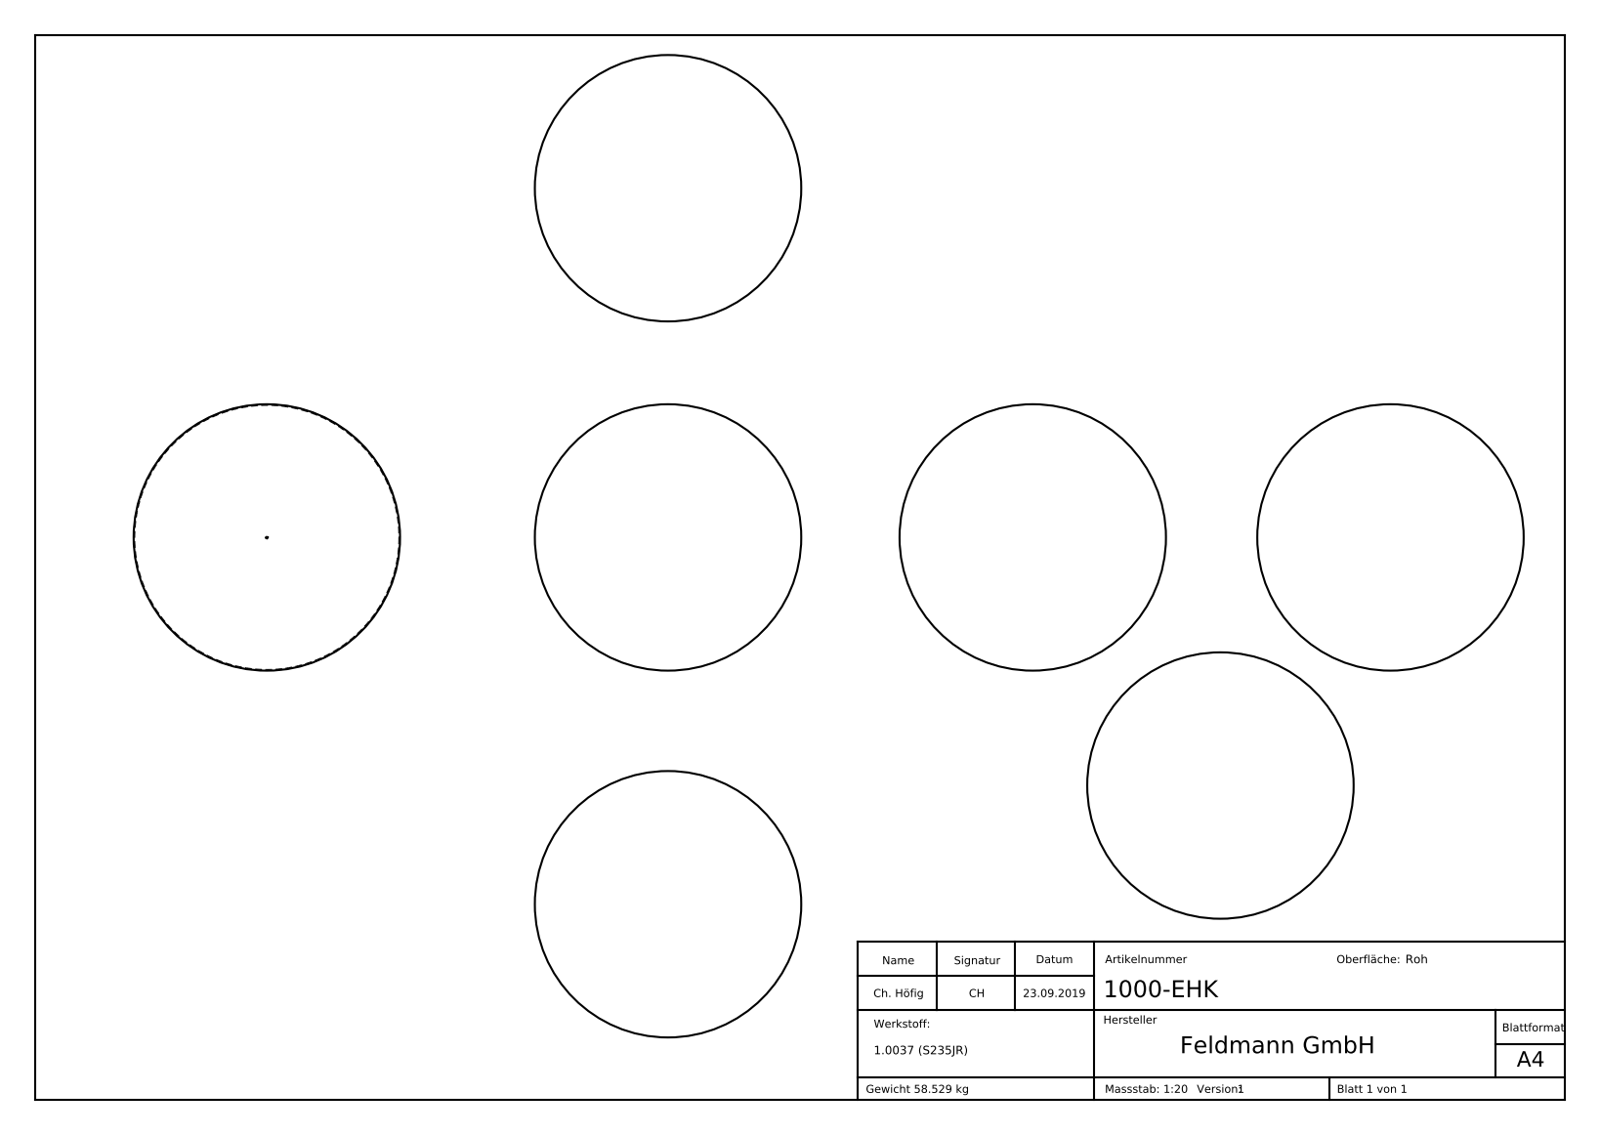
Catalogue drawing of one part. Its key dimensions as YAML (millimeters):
part_name: "1000-EHK"
step_written_by: "SolidWorks 2015 (CONFIG_CONTROL_DESIGN)"
units: millimeters
bodies: {solids: 1, faces: 201, planar: 99, cylindrical: 0, other: 102}
overall_size: [1000, 1000, 1000]
volume: 7504000
surface_area: 6253000
face_to_face_distances: [1.26, 0.74, 0.46, 3.98, 4.1, 0.68, 3.2, 0.4, 0.54, 0.86]
